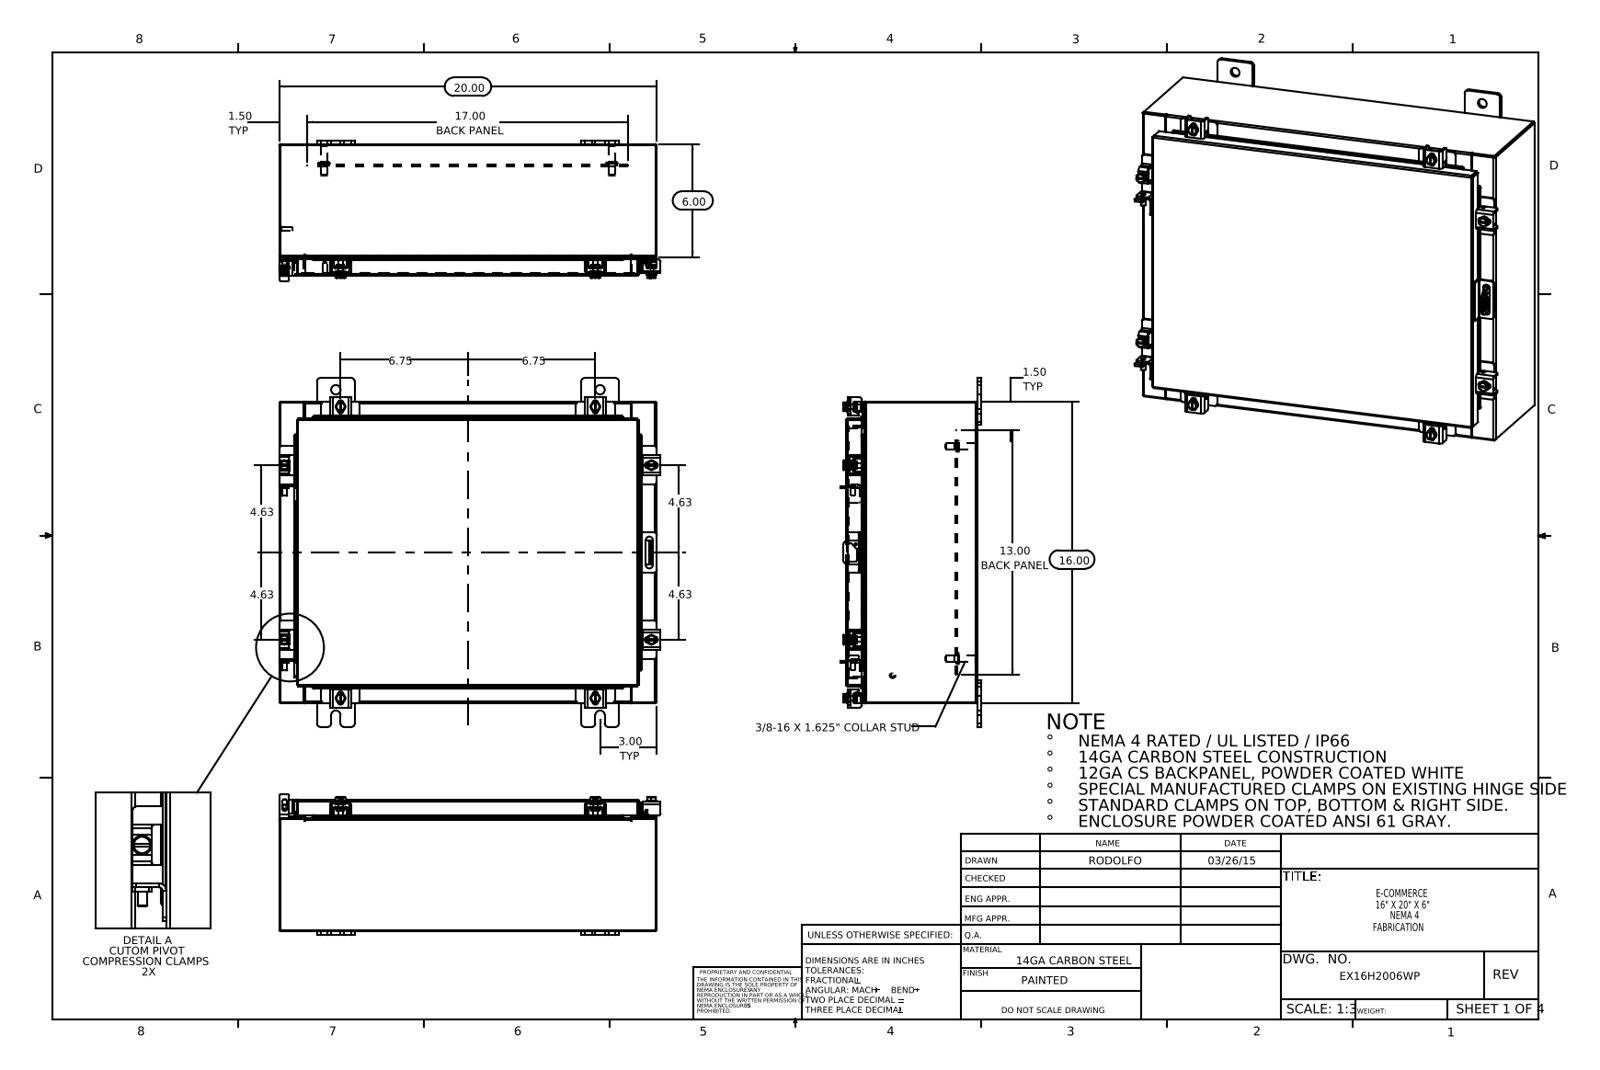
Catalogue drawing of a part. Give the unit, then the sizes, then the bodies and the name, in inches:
Units: inches
Overall size (bounding box): 20.211 × 18.5 × 7.453
Round holes (diameter × count): ⌀0.213 ×8, ⌀0.26 ×8, ⌀0.5 ×8, ⌀0.125 ×1, ⌀0.25 ×1
Round bosses / shafts (diameter × count): ⌀0.5 ×8, ⌀0.25 ×8, ⌀0.399 ×6, ⌀0.625 ×4, ⌀0.375 ×4, ⌀0.33 ×4, ⌀0.315 ×2, ⌀0.236 ×2
Partial cylindrical surfaces — rounded edges, fillets, slot ends (radius × count): R0.06 ×34, R0.19 ×24, R0.013 ×22, R0.088 ×22, R0.1 ×16, R0.09 ×14, R0.12 ×14, R0.141 ×12
Main face-to-face distances: 0.075, 6.9, 6.975, 6.826, 15.925, 1, 1.075, 5.826, 5.9, 1.179
Hole centre spacings: 13.38, 16.765, 19.619, 4.297, 10.463, 12.704, 20.591, 0.43
Volume: 121.3 in³ · Surface area: 3 044 in²
Bodies: 59 solids, 1468 faces (791 planar, 549 cylindrical, 128 other)
Part name (STEP PRODUCT): ATEX CLAMP HINGE BRAKET; HW-CLN-NH-20320; EX16H2006WP Padlock Hasp; 22104005_DEFAULT_RTP30 (+8 more)
STEP written by: SolidWorks 2014 (CONFIG_CONTROL_DESIGN)
